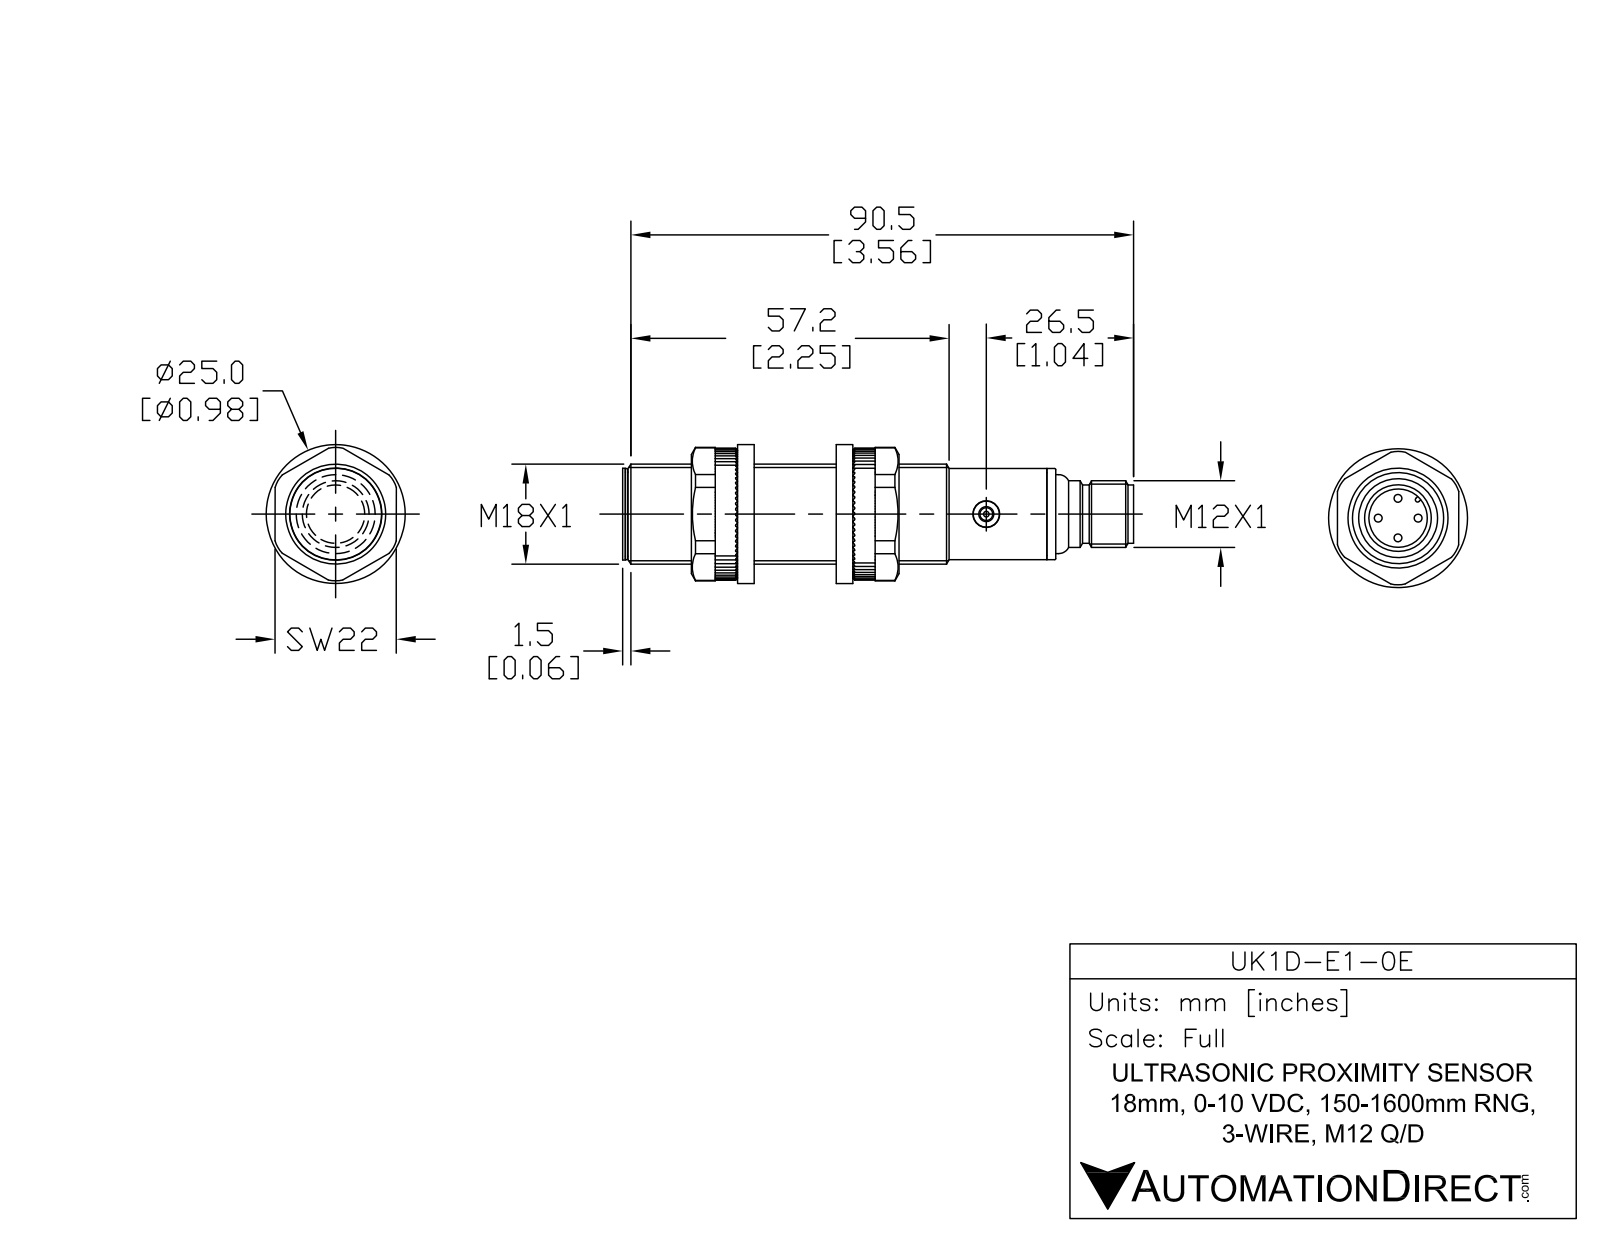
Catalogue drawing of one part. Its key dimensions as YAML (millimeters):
part_name: "UK1D-E1-0E"
step_written_by: "SolidWorks 2017 (AUTOMOTIVE_DESIGN)"
units: millimeters
bodies: {solids: 6, faces: 106, planar: 21, cylindrical: 48, other: 37}
overall_size: [91.6, 18, 18]
volume: 19700
surface_area: 6890
round_holes:
  - {diameter: 2.7, count: 1}
  - {diameter: 4.7, count: 1}
  - {diameter: 7, count: 1}
  - {diameter: 8.3, count: 1}
  - {diameter: 9.5, count: 1}
round_bosses_or_shafts:
  - {diameter: 1, count: 4}
  - {diameter: 18, count: 1}
  - {diameter: 16.6, count: 1}
  - {diameter: 16.4, count: 1}
  - {diameter: 15.8, count: 1}
  - {diameter: 14.2, count: 1}
  - {diameter: 12, count: 1}
  - {diameter: 10.5, count: 1}
partial_cylinders:
  - {radius: 0.6, count: 1}
face_to_face_distances: [75.1, 1, 76.1, 0.9, 76, 1.1, 4, 77.6, 77.5, 76.6]
